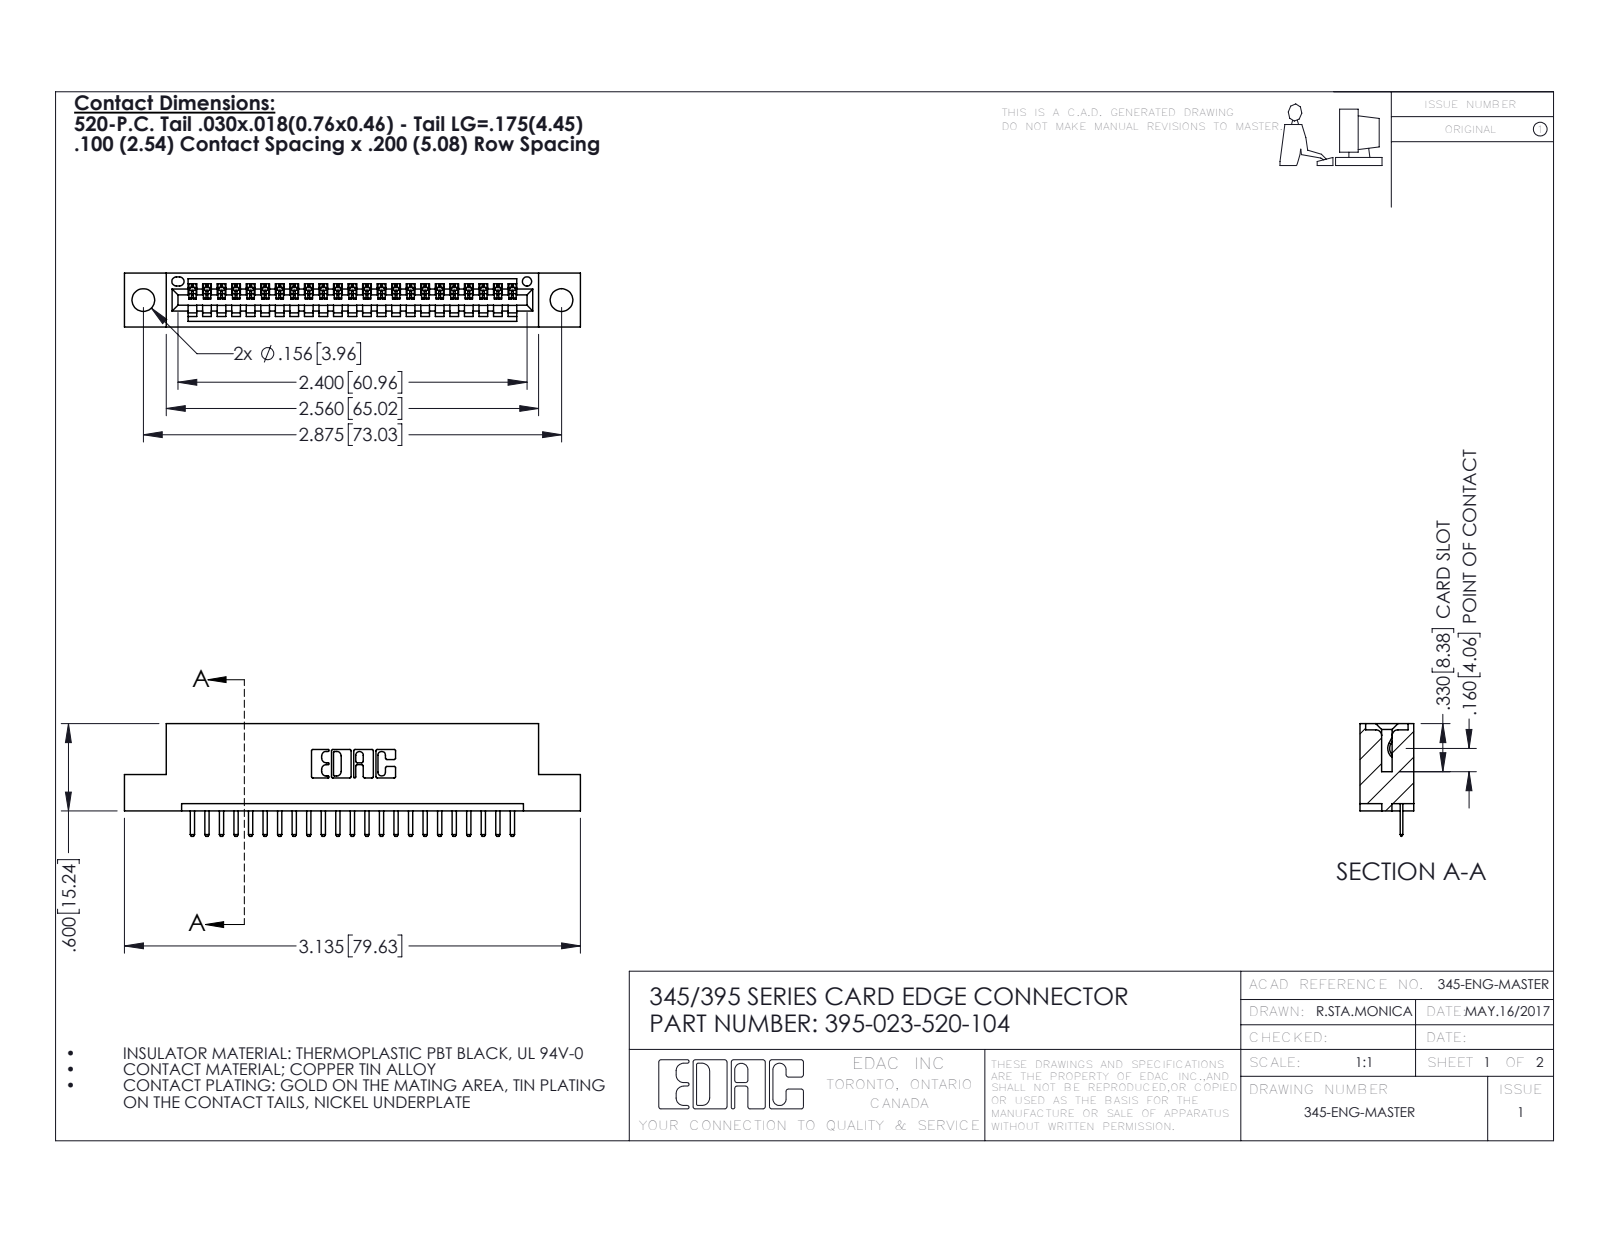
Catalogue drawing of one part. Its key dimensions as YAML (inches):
part_name: "345 Part_Flush Mounting Lugs - 0.156 Dia-TH; 395-023-520-104; 345-292-001_345-293-120"
step_written_by: "SolidWorks 2016 (CONFIG_CONTROL_DESIGN)"
units: inches
bodies: {solids: 24, faces: 1552, planar: 1046, cylindrical: 506, other: 0}
overall_size: [3.135, 0.775, 0.37]
volume: 0.443
surface_area: 13.91
round_holes:
  - {diameter: 0.156, count: 2}
  - {diameter: 0.064, count: 1}
partial_cylinders:
  - {radius: 0.01, count: 48}
  - {radius: 0.006, count: 46}
  - {radius: 0.01, count: 22}
  - {radius: 0.007, count: 6}
  - {radius: 0.031, count: 6}
  - {radius: 0.026, count: 3}
  - {radius: 0.031, count: 2}
  - {radius: 0.04, count: 2}
face_to_face_distances: [0.298, 0.072, 0.37, 0.2, 0.098, 0.272, 0.025, 0.225, 0.072, 0.149]
hole_center_spacings: [0.27, 2.641, 2.875]
